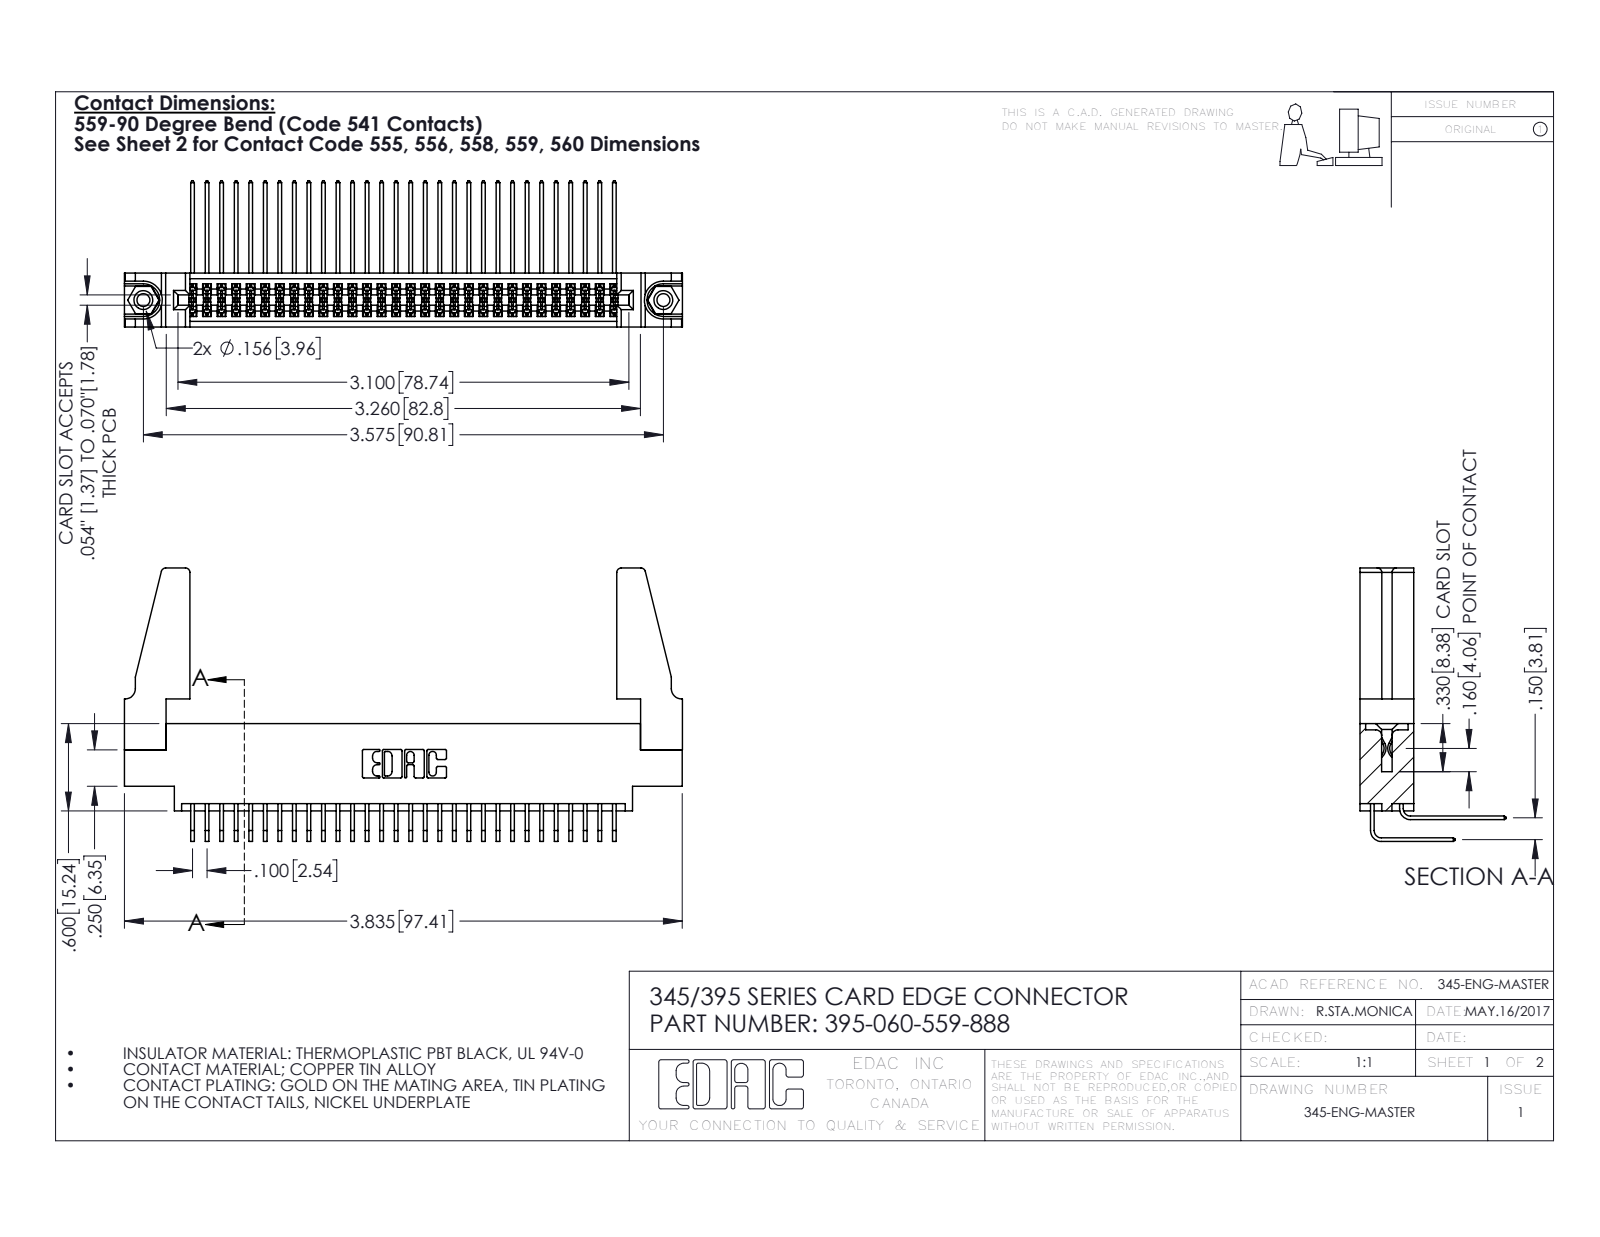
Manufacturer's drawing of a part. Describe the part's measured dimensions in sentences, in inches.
The part is named "345-292-001_558 559 Tail - 1; 345-220-078_345-220-088; 395-060-559-888; 345-250-001_345-250-001-102 (+2 more)". Its 3-D file was written by "SolidWorks 2016 (CONFIG_CONTROL_DESIGN)". It is 65 solids with 3374 faces: 2256 planar, 1102 cylindrical and 16 other. Overall it measures 3.836 by 1.879 by 1.005 inches. Its volume is 0.783 cubic inches and its surface area 29.19 square inches. Round holes: 2 of diameter 0.089, 2 of diameter 0.125, 2 of diameter 0.156, 1 of diameter 0.064. Round bosses or shafts: 2 of diameter 0.155. Partial cylindrical surfaces (rounded edges, fillets, slot ends): 90 of radius 0.006, 22 of radius 0.01, 8 of radius 0.03, 6 of radius 0.007, 6 of radius 0.031, 3 of radius 0.026, 2 of radius 0.014, 2 of radius 0.019. The main face-to-face distances are 0.072, 0.37, 0.298, 0.2, 0.098, 0.272, 0.025, 0.225, 0.15, 0.175. The hole center spacings are 0.27, 3.34, 3.575.
